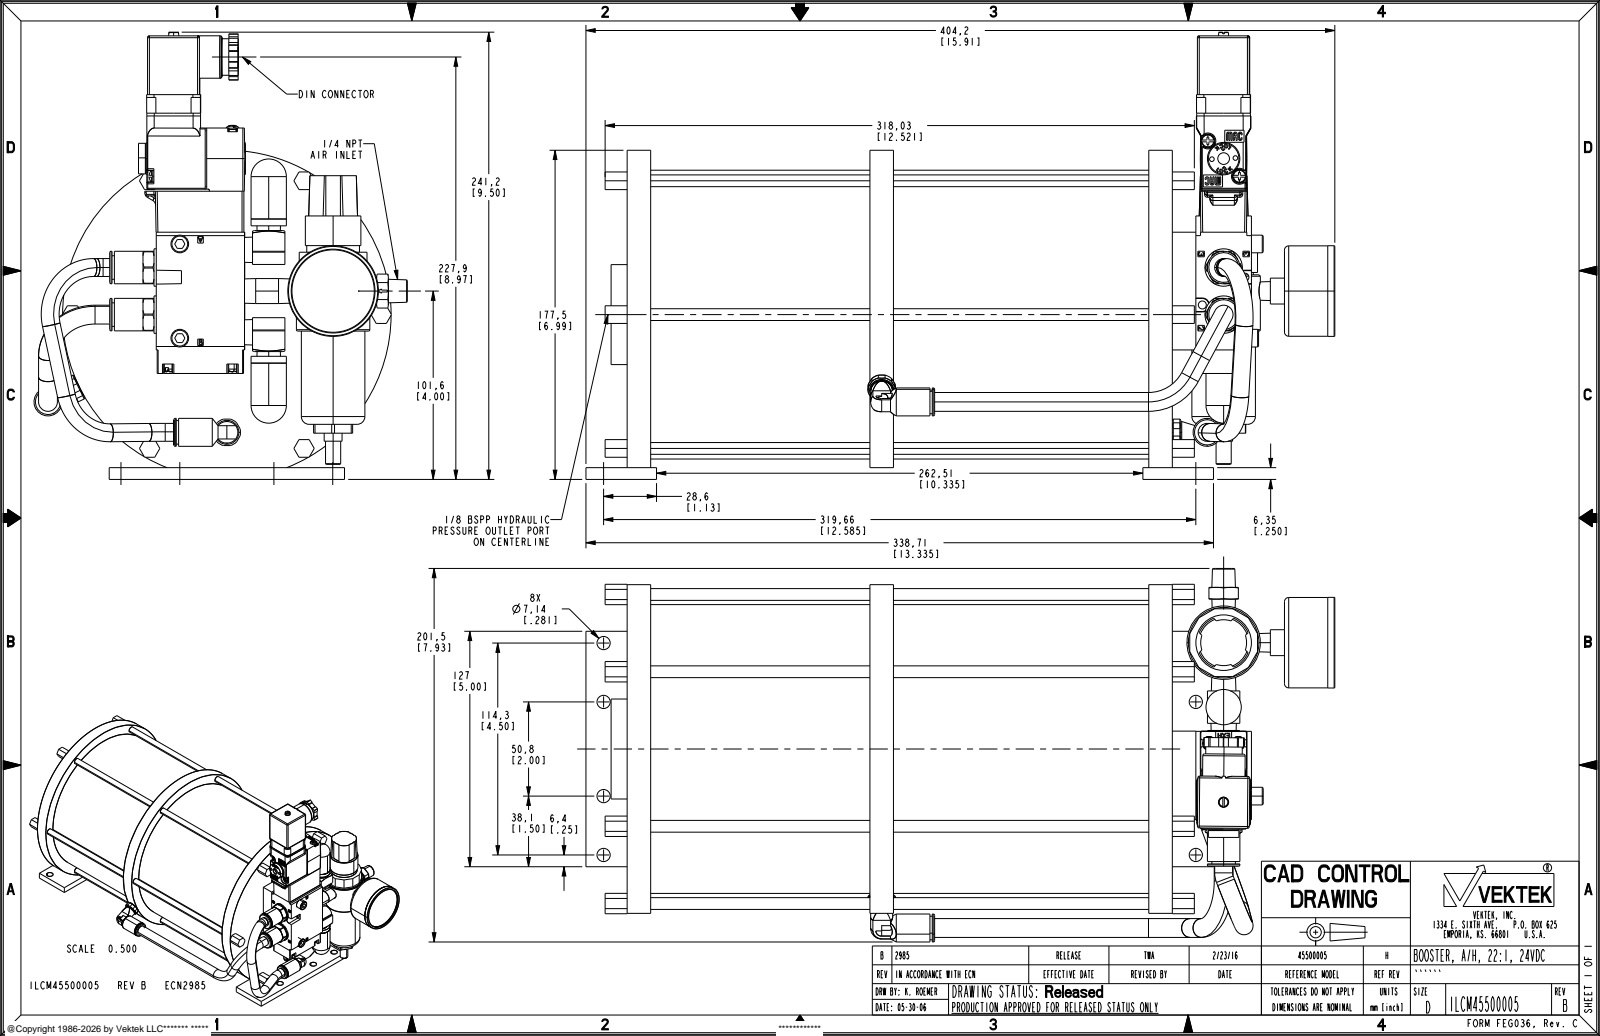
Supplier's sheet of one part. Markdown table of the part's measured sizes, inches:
| quantity | value |
| --- | --- |
| part name | ILCM45500005 |
| STEP written by | PRO/ENGINEER BY PARAMETRIC TECHNOLOGY CORPORATION, 2013320 (CONFIG_CONTROL_DESIGN) |
| units | inches |
| bodies | 1 solid, 1437 faces (695 planar, 424 cylindrical, 318 other) |
| overall size | 15.913 × 9.498 × 7.933 |
| volume | 365 in³ |
| surface area | 603.5 in² |
| round holes (diameter × count) | 0.281 × 12, 0.201 × 4, 0.213 × 2, 0.262 × 2, 0.276 × 2, 0.5 × 2, 0.54 × 2, 0.65 × 2, 0.69 × 2, 0.794 × 2, 0.145 × 1, 0.256 × 1 |
| round bosses / shafts (diameter × count) | 0.25 × 12, 0.38 × 6, 0.579 × 5, 0.4 × 4, 0.375 × 4, 0.46 × 3, 0.594 × 2, 0.5 × 2 |
| partial cylindrical surfaces (radius × count) | 0.039 × 20, 0.01 × 14, 0.008 × 13, 0.031 × 13, 0.157 × 12, 0.02 × 11, 0.043 × 8, 0.041 × 6 |
| main face-to-face distances | 11.585, 0.5, 11.085, 5.159, 5.926, 0.25, 6.426, 5.659, 4.659, 10.585 |
| hole center spacings | 2, 0.75, 1.25, 1.458, 2.136, 3.25, 3.335, 11.835 |
